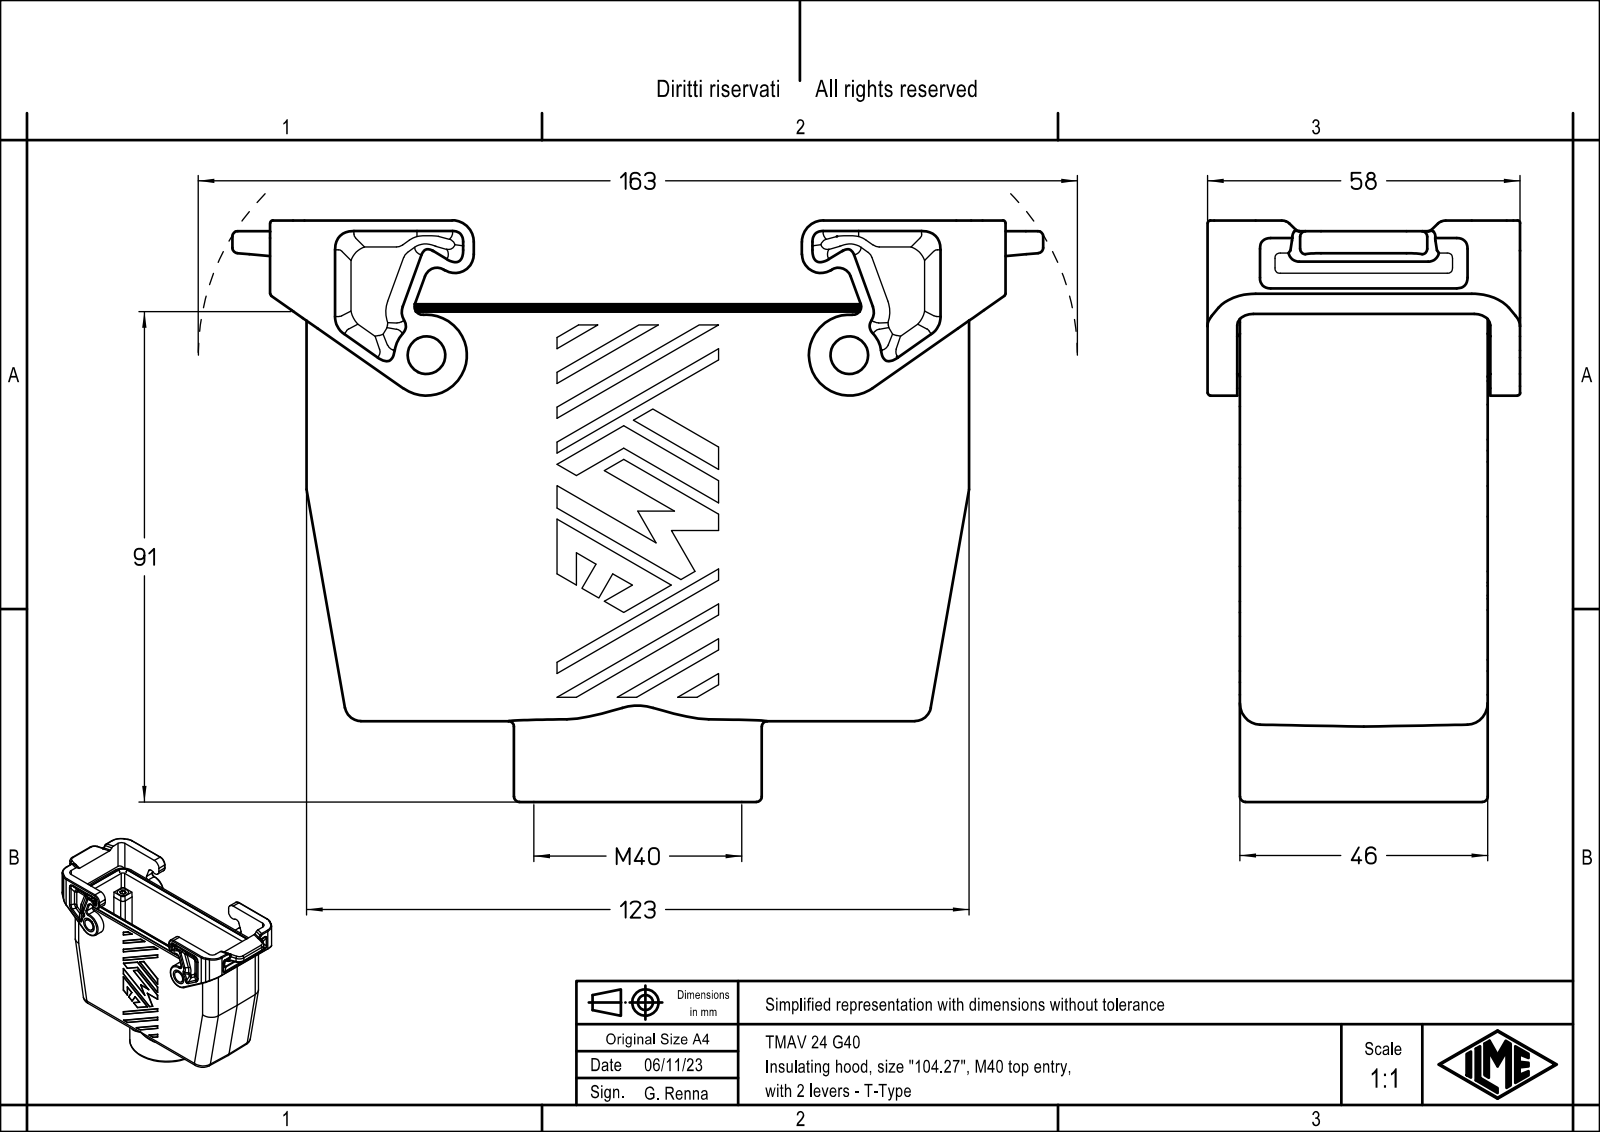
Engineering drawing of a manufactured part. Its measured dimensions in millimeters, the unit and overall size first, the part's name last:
Units: millimetres
Overall size (bounding box): 150.5 × 107.9 × 58
Round holes (diameter × count): ⌀34 ×1, ⌀38.6 ×1
Round bosses / shafts (diameter × count): ⌀7 ×2, ⌀46 ×1
Partial cylindrical surfaces — rounded edges, fillets, slot ends (radius × count): R0.15 ×88, R3 ×20, R1 ×16, R2 ×16, R1.5 ×10, R1.3 ×8, R6 ×8, R7 ×8
Main face-to-face distances: 5.4, 40.6, 35.2, 46, 0.5, 5.9, 41.1, 46.5, 5.5, 52
Volume: 179 658 mm³ · Surface area: 70 873 mm²
Bodies: 1 solid, 562 faces (218 planar, 282 cylindrical, 62 other)
Part name (STEP PRODUCT): TMAV 24 G40
STEP written by: Creo Elements/Direct Modeling 20.1B 02-Apr-2019 (C) Parametric Technology GmbH (AUTOMOTIVE_DESIGN)
